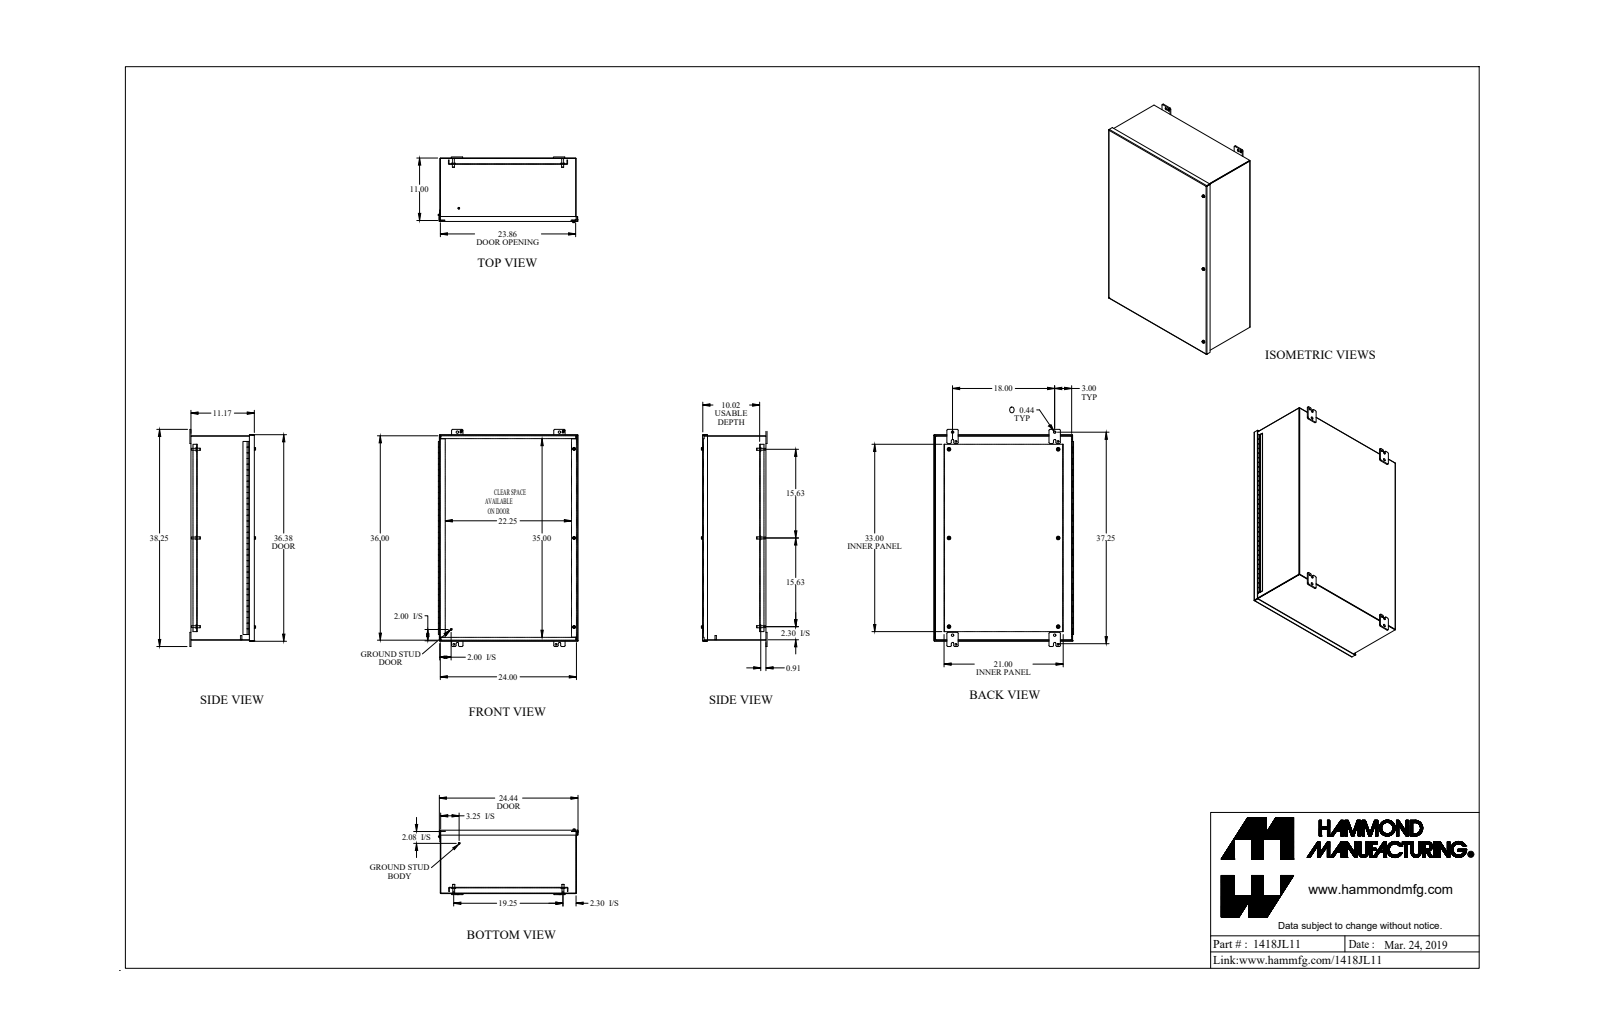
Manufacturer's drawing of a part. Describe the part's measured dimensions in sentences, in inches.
The part is named "1418JL11_Default". Its 3-D file was written by "SolidWorks 2018 (CONFIG_CONTROL_DESIGN)". It is 44 solids with 1149 faces: 676 planar, 411 cylindrical and 62 other. Overall it measures 38.25 by 24.604 by 11.571 inches. Its volume is 343.5 cubic inches and its surface area 8 596 square inches. Round holes: 7 of diameter 0.313, 6 of diameter 0.5, 4 of diameter 0.307, 4 of diameter 0.437, 4 of diameter 0.445, 3 of diameter 0.26, 3 of diameter 0.266, 3 of diameter 0.28, 3 of diameter 0.29, 3 of diameter 0.397, 1 of diameter 0.187, 1 of diameter 3.5. Round bosses or shafts: 6 of diameter 0.65, 6 of diameter 0.375, 6 of diameter 0.33, 4 of diameter 1, 3 of diameter 0.51, 3 of diameter 0.5, 3 of diameter 0.39, 3 of diameter 0.244. Partial cylindrical surfaces (rounded edges, fillets, slot ends): 24 of radius 0.188, 20 of radius 0.25, 10 of radius 0.036, 10 of radius 0.108, 8 of radius 0.218, 6 of radius 0.133, 5 of radius 0.06, 5 of radius 0.125. The main face-to-face distances are 0.072, 11.1, 11.172, 11.028, 23.928, 0.095, 9.996, 1.104, 1.032, 10.068. The hole center spacings are 31.25, 36.703, 19.25, 1.735, 3.065, 15.625, 15.625, 15.687.
